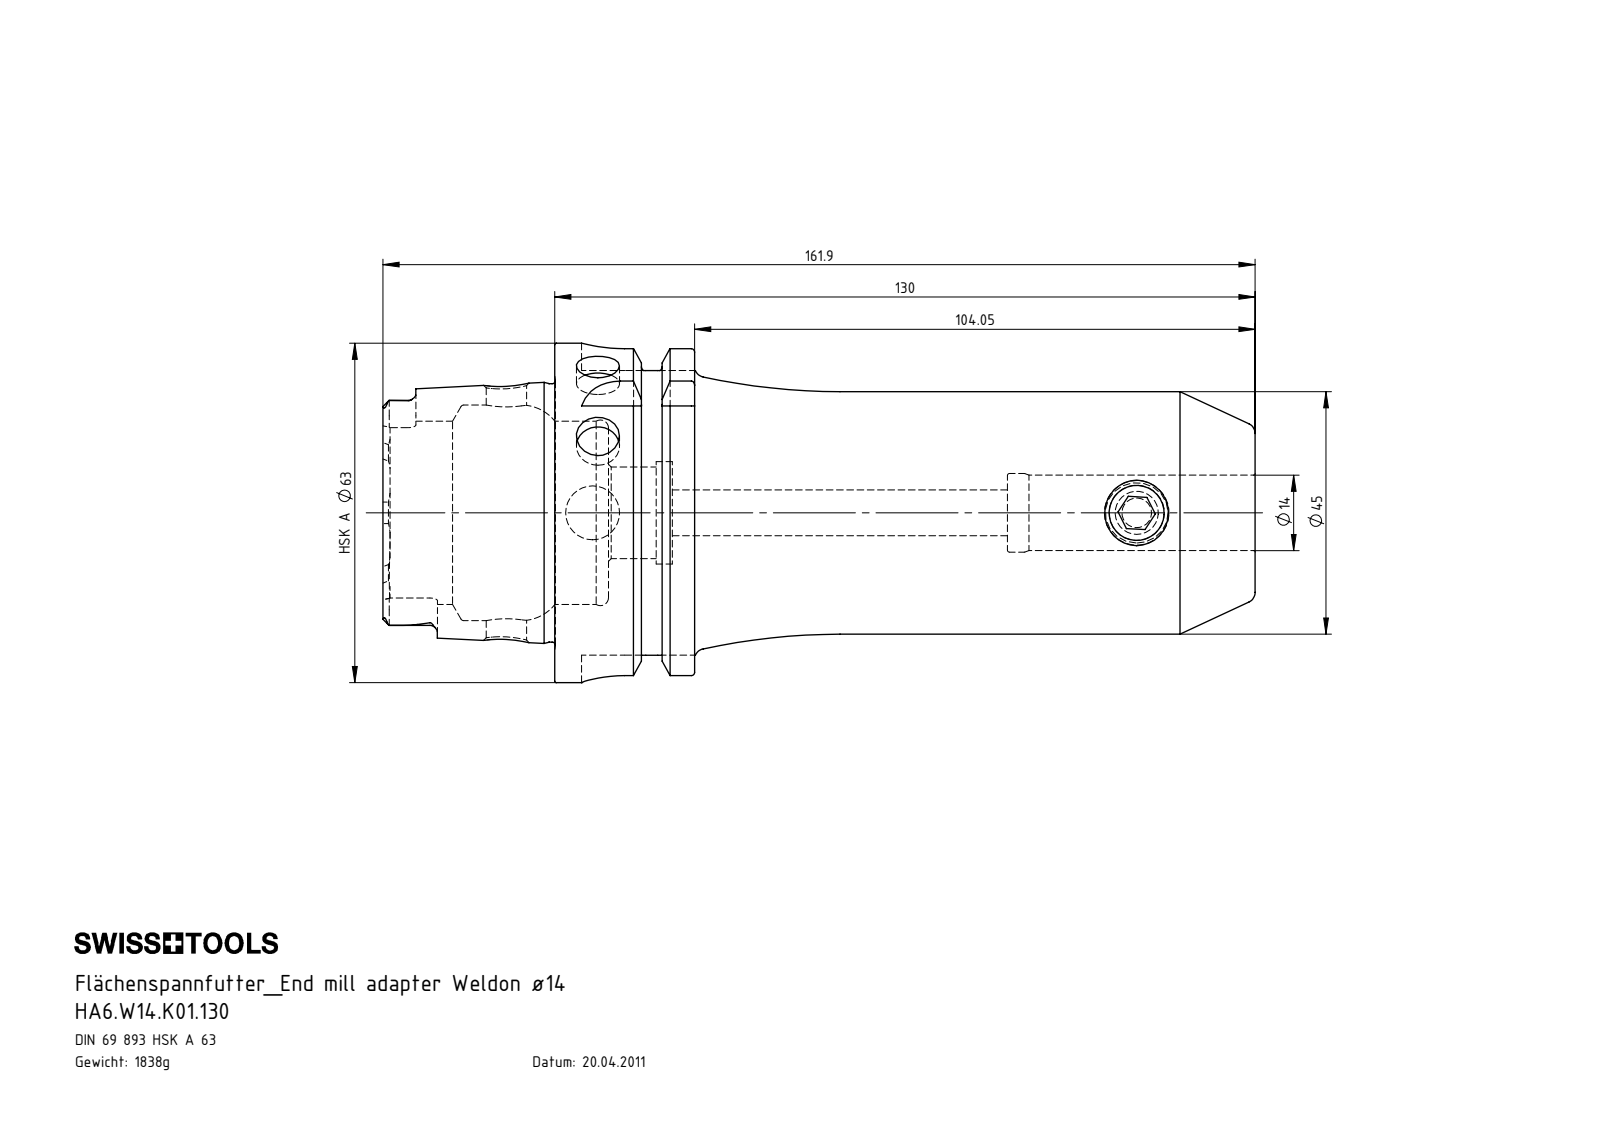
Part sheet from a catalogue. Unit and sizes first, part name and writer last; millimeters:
Units: millimetres
Overall size (bounding box): 161.9 × 63 × 63
Round holes (diameter × count): ⌀8 ×2, ⌀7.5 ×1, ⌀8.5 ×1, ⌀10 ×1, ⌀10.25 ×1, ⌀14 ×1, ⌀14.6 ×1, ⌀17 ×1, ⌀19 ×1, ⌀34 ×1, ⌀40 ×1
Round bosses / shafts (diameter × count): ⌀63 ×1, ⌀54.95 ×1, ⌀47.94 ×1, ⌀45 ×1, ⌀12 ×1
Partial cylindrical surfaces — rounded edges, fillets, slot ends (radius × count): R1.4 ×6, R2.88 ×4, R8 ×4
Main face-to-face distances: 16, 25.95, 9.95, 130, 120.05, 104.05, 31.9, 41.85, 57.85, 161.9
Hole centre spacings: 101
Volume: 234 139 mm³ · Surface area: 40 779 mm²
Bodies: 2 solids, 211 faces (59 planar, 57 cylindrical, 95 other)
Part name (STEP PRODUCT): W12-ER1.001.016; HA6-W14.K01.130; HA6-W14.K01.130_A_Fertigbearbeitung
STEP written by: SolidWorks 2012 (CONFIG_CONTROL_DESIGN)
